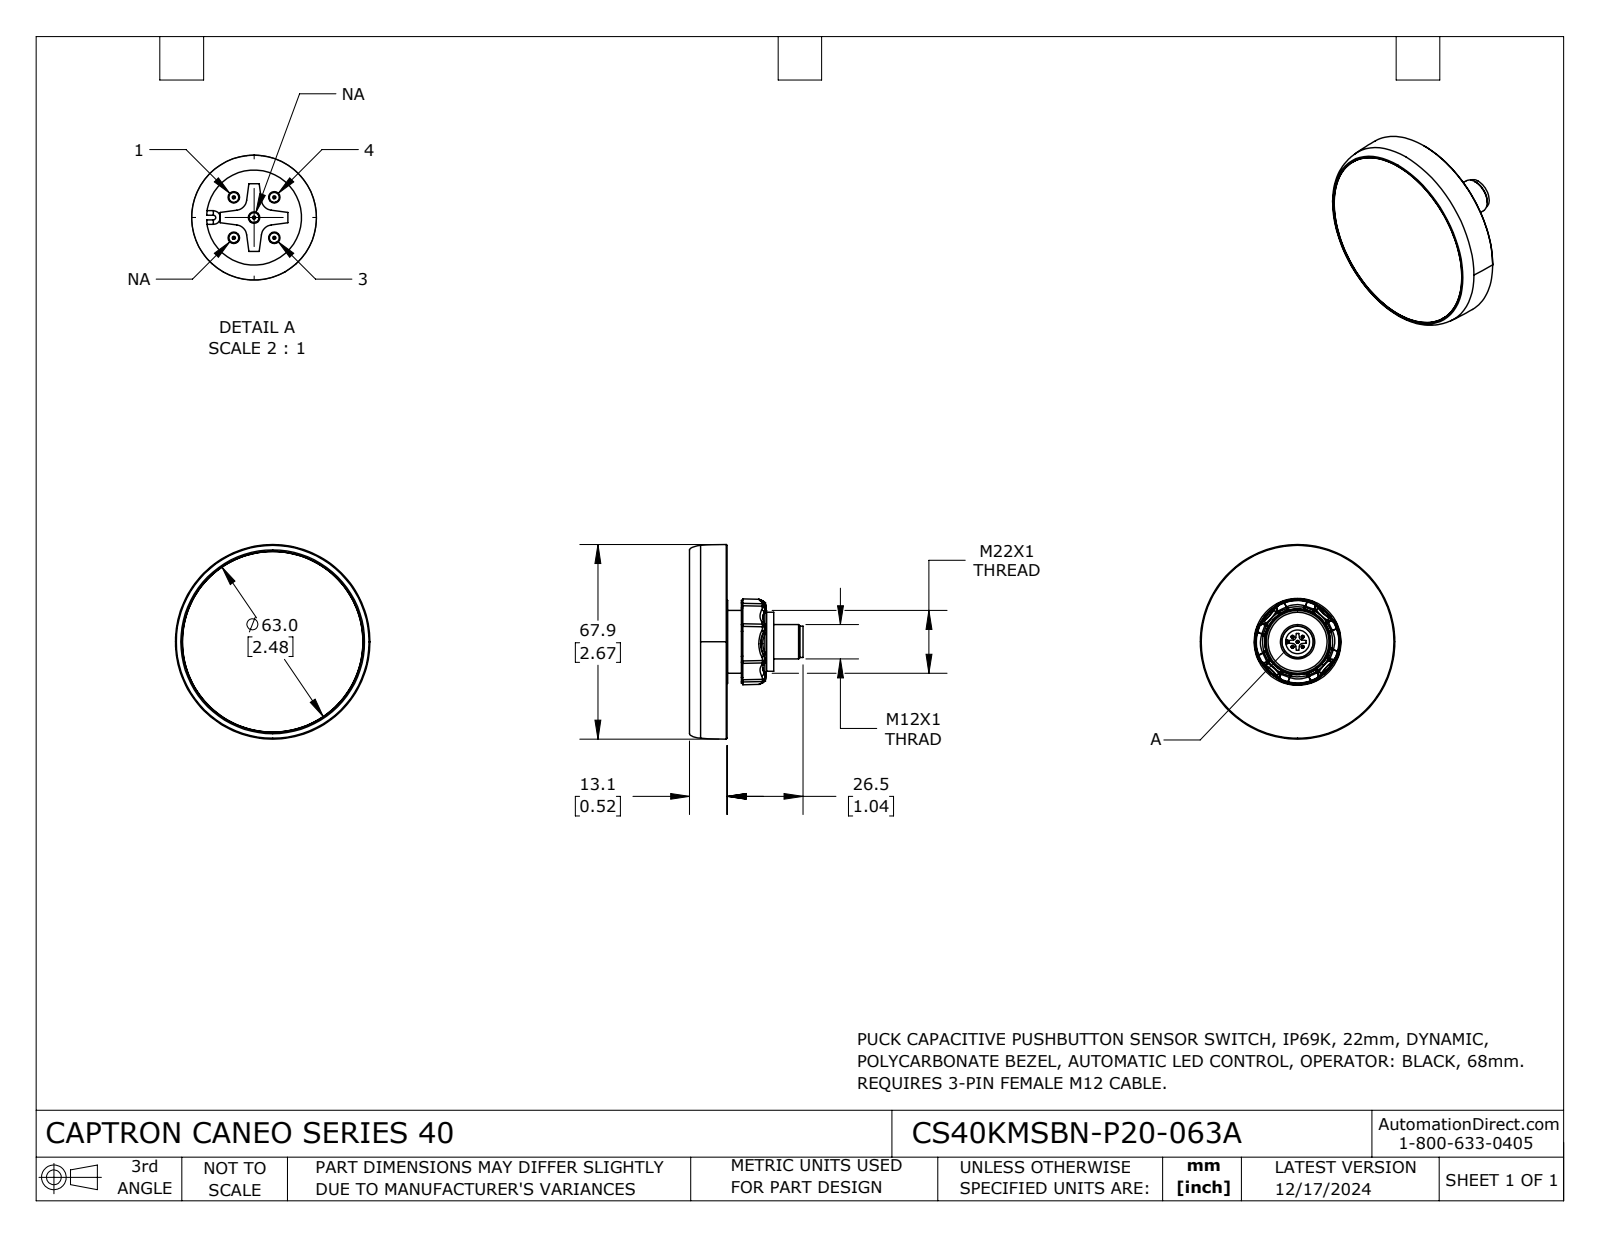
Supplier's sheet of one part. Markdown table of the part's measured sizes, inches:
| quantity | value |
| --- | --- |
| part name | CS40KMSBN-P20-063A |
| STEP written by | SolidWorks 2024 (CONFIG_CONTROL_DESIGN) |
| units | inches |
| bodies | 3 solids, 420 faces (62 planar, 50 cylindrical, 308 other) |
| overall size | 2.673 × 2.673 × 1.559 |
| volume | 3.397 in³ |
| surface area | 23.2 in² |
| round holes (diameter × count) | 0.327 × 1, 0.827 × 1, 0.927 × 1, 1.193 × 1, 2.484 × 1 |
| round bosses / shafts (diameter × count) | 0.039 × 5, 2.48 × 1, 0.862 × 1, 0.811 × 1, 0.472 × 1, 0.429 × 1 |
| partial cylindrical surfaces (radius × count) | 0.295 × 8, 0.039 × 4, 0.689 × 4, 0.016 × 2, 0.024 × 1 |
| main face-to-face distances | 0.516, 0.02, 0.496, 0.642, 0.661, 1.157, 0.217, 0.713, 0.197, 0.659 |
